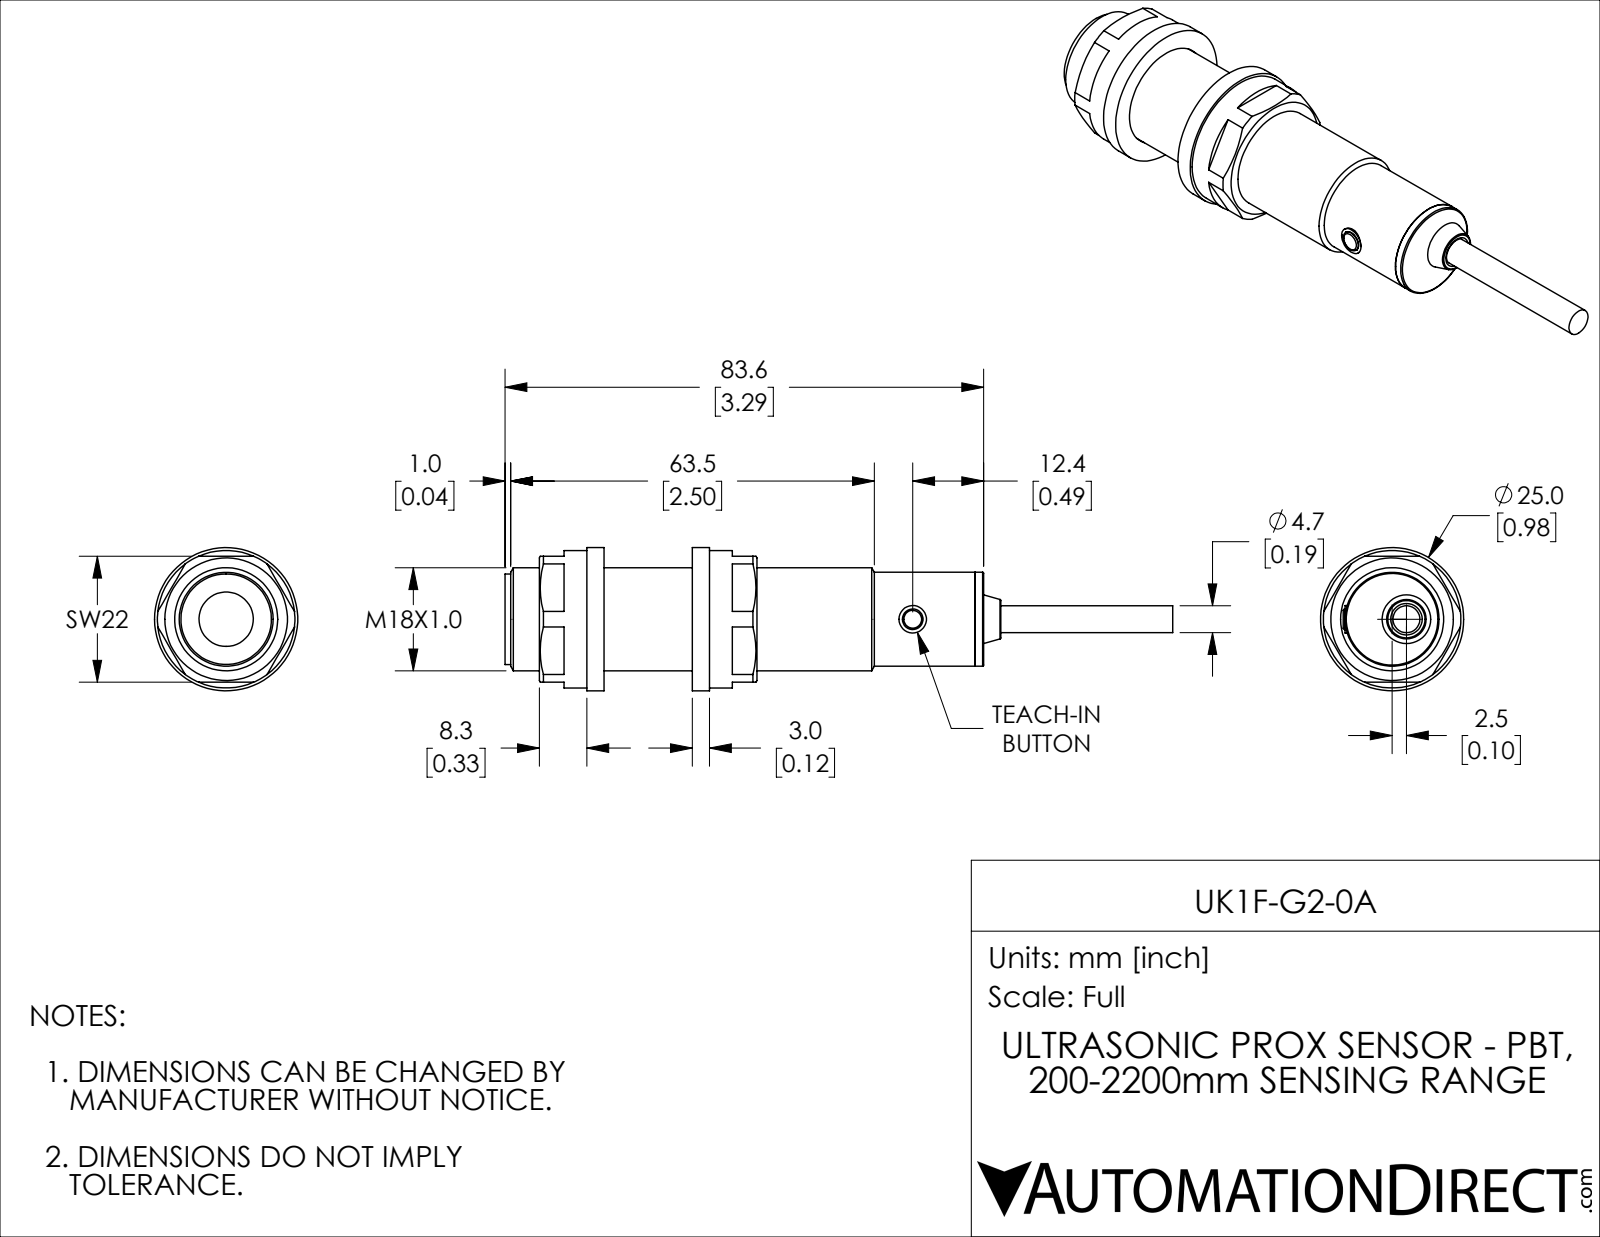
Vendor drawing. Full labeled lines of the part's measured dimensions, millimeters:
Part name (STEP PRODUCT): UK1F-G2-0A
STEP written by: SolidWorks 2018 (AUTOMOTIVE_DESIGN)
Units: millimetres
Bodies: 10 solids, 107 faces (49 planar, 40 cylindrical, 18 other)
Overall size (bounding box): 116.6 × 25 × 25
Volume: 25 220 mm³ · Surface area: 11 419 mm²
Round holes (diameter × count): ⌀4.7 ×2, ⌀3.6 ×1, ⌀9.5 ×1, ⌀18 ×1, ⌀18.2 ×1
Round bosses / shafts (diameter × count): ⌀25 ×1, ⌀24 ×1, ⌀16.4 ×1, ⌀15.8 ×1, ⌀5.4 ×1, ⌀4.8 ×1
Main face-to-face distances: 3, 18.4, 21.4, 67.8, 46.4, 13.3, 34.7, 81.1, 16.3, 64.8
Hole centre spacings: 2.5
